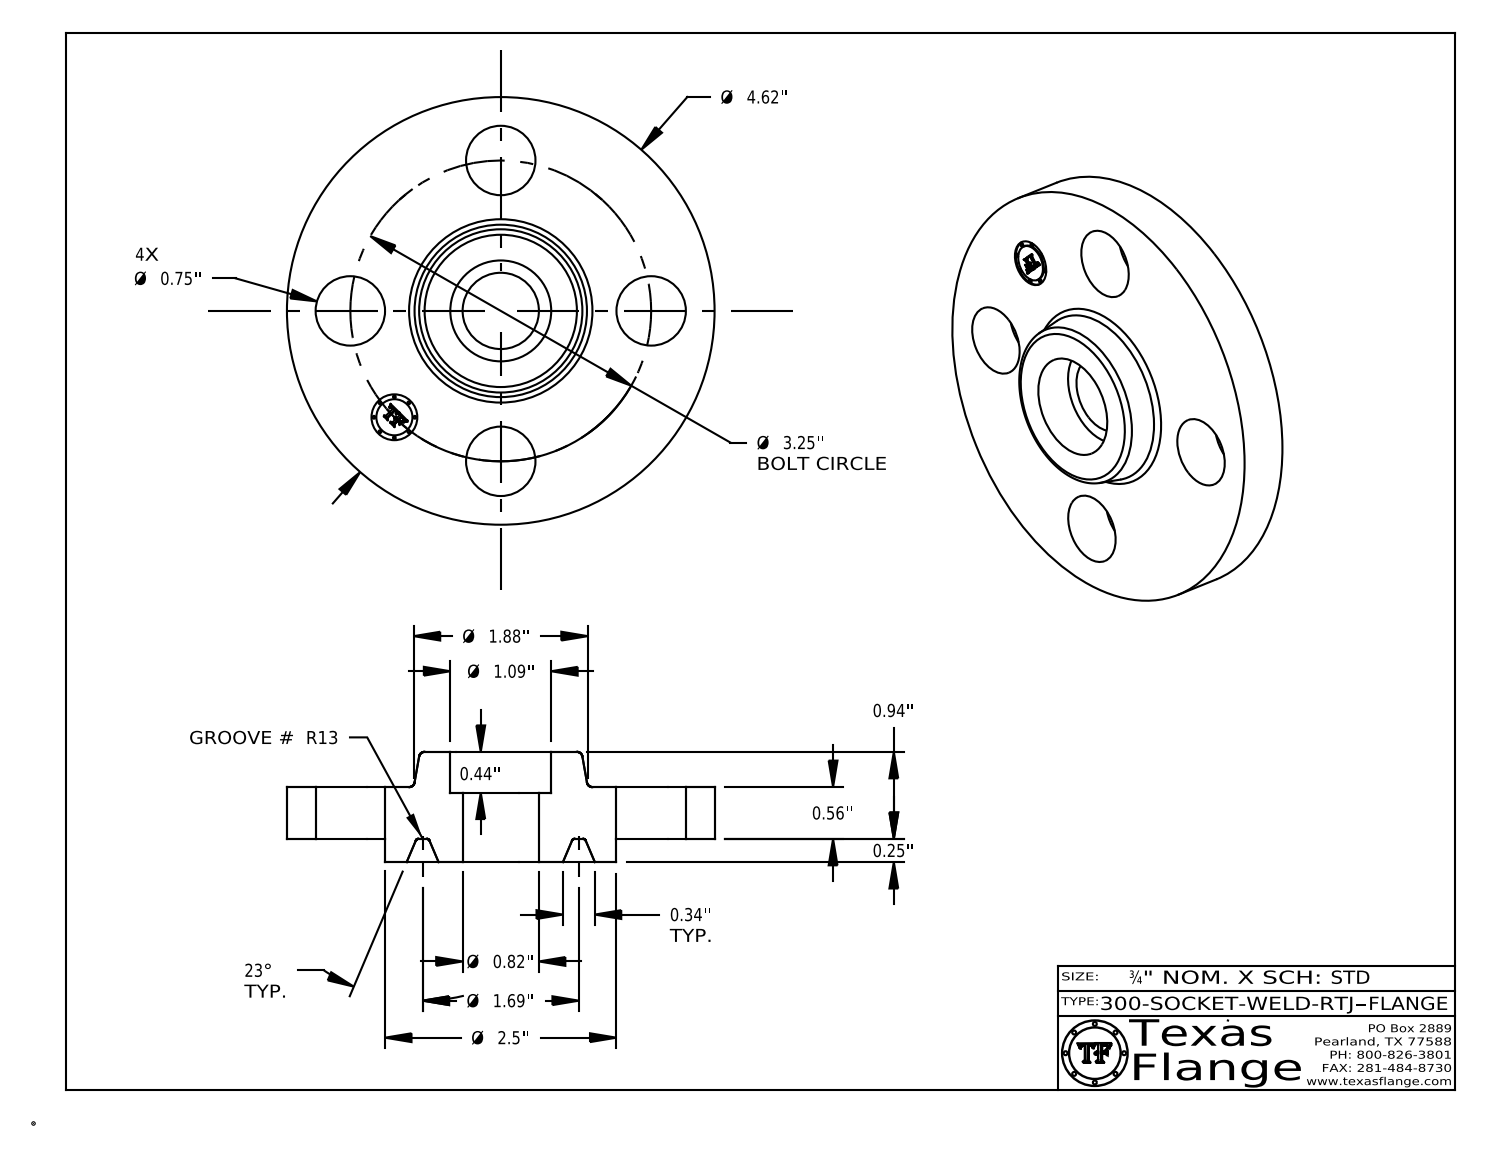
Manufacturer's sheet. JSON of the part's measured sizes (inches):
{"part_name": "300-SOCKET-WELD-RTJ", "step_written_by": "CATIA V5 STEP AP214 (AUTOMOTIVE_DESIGN)", "units": "inches", "bodies": {"solids": 1, "faces": 422, "planar": 372, "cylindrical": 36, "other": 14}, "overall_size": [4.62, 4.62, 1.19], "volume_in3": 9.481, "surface_area_in2": 51.17, "round_holes": [[0.75, 4], [0.495, 1], [0.824, 1], [1.09, 1]], "round_bosses_or_shafts": [[0.03, 8], [4.62, 1], [2.5, 1], [0.39, 1]], "face_to_face_distances": [0.56, 0.25, 0.81, 1.19, 0.94, 0.38, 0.75, 0.5, 0.06, 0.44], "hole_center_spacings": [1.625, 2.298, 1.244, 3.003, 3.25]}
